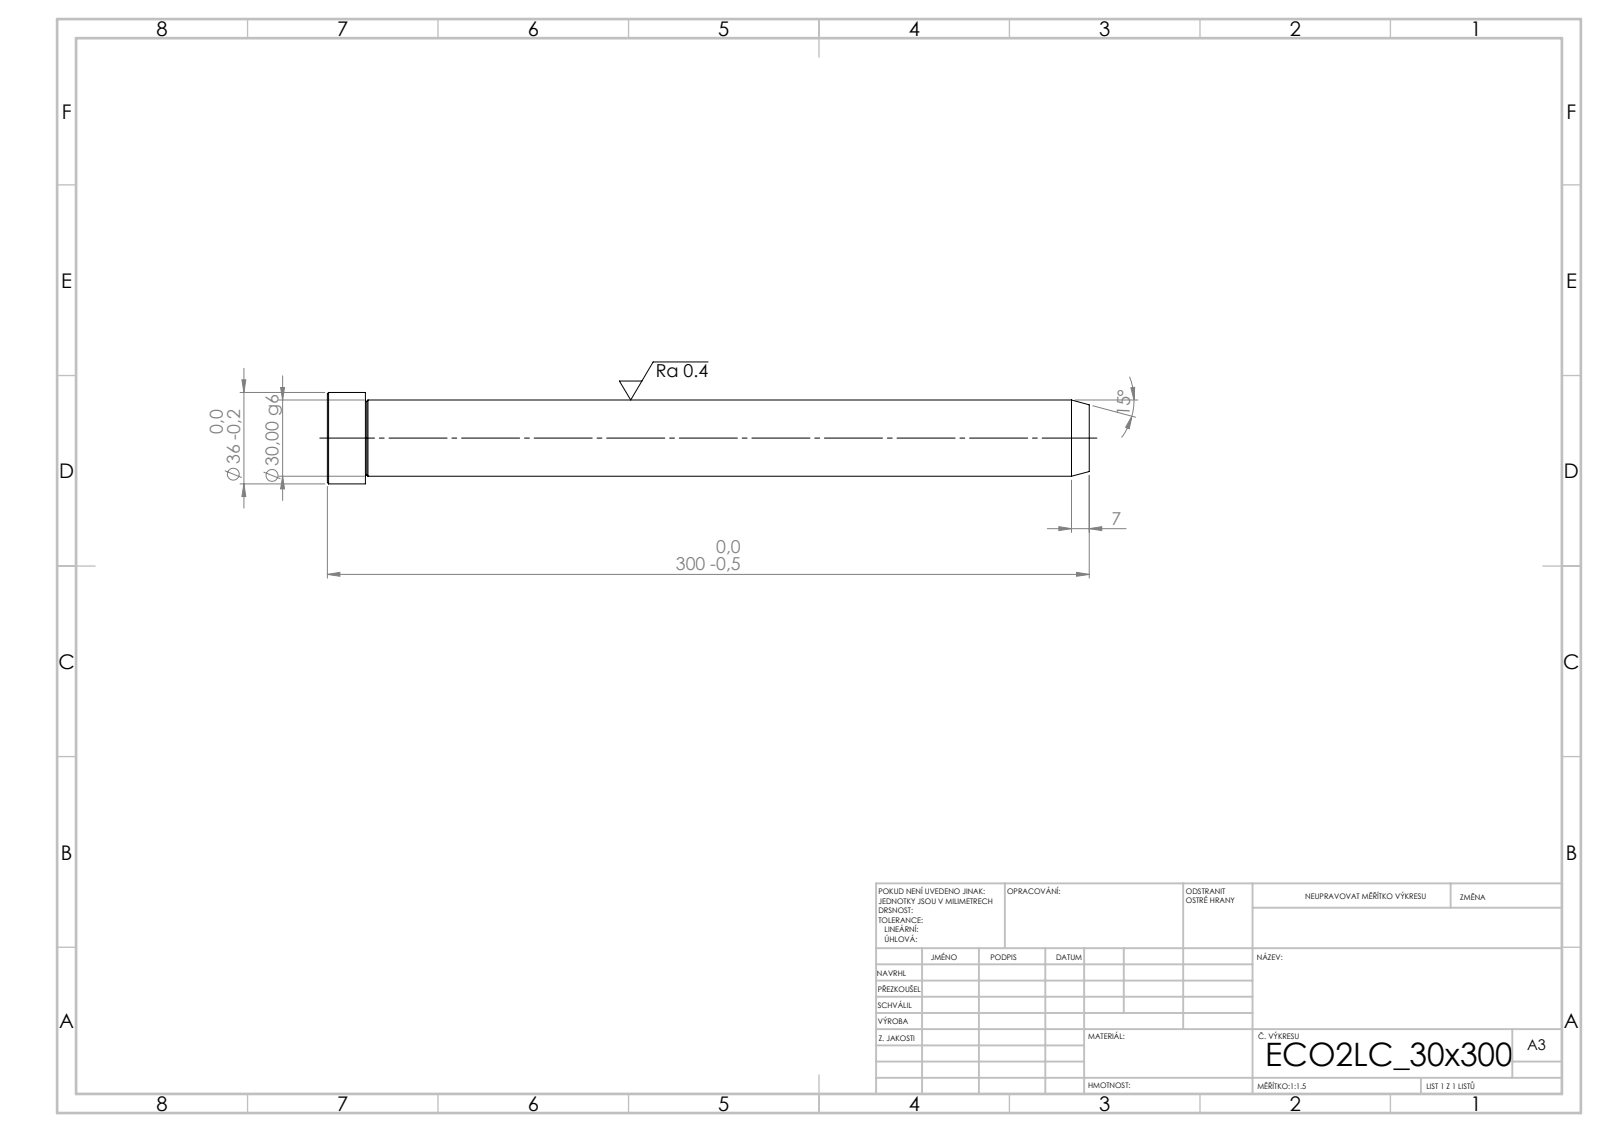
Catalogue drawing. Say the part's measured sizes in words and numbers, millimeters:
Its 3-D file was written by "SolidWorks 2019 (CONFIG_CONTROL_DESIGN)". It is 1 solid with 15 faces: 3 planar, 4 cylindrical and 8 other. Overall it measures 300 by 36 by 36 millimeters. Its volume is 216 079 cubic millimeters and its surface area 30 425 square millimeters. Round bosses or shafts: 1 of diameter 36, 1 of diameter 30. The main face-to-face distances are 300, 285, 15.
